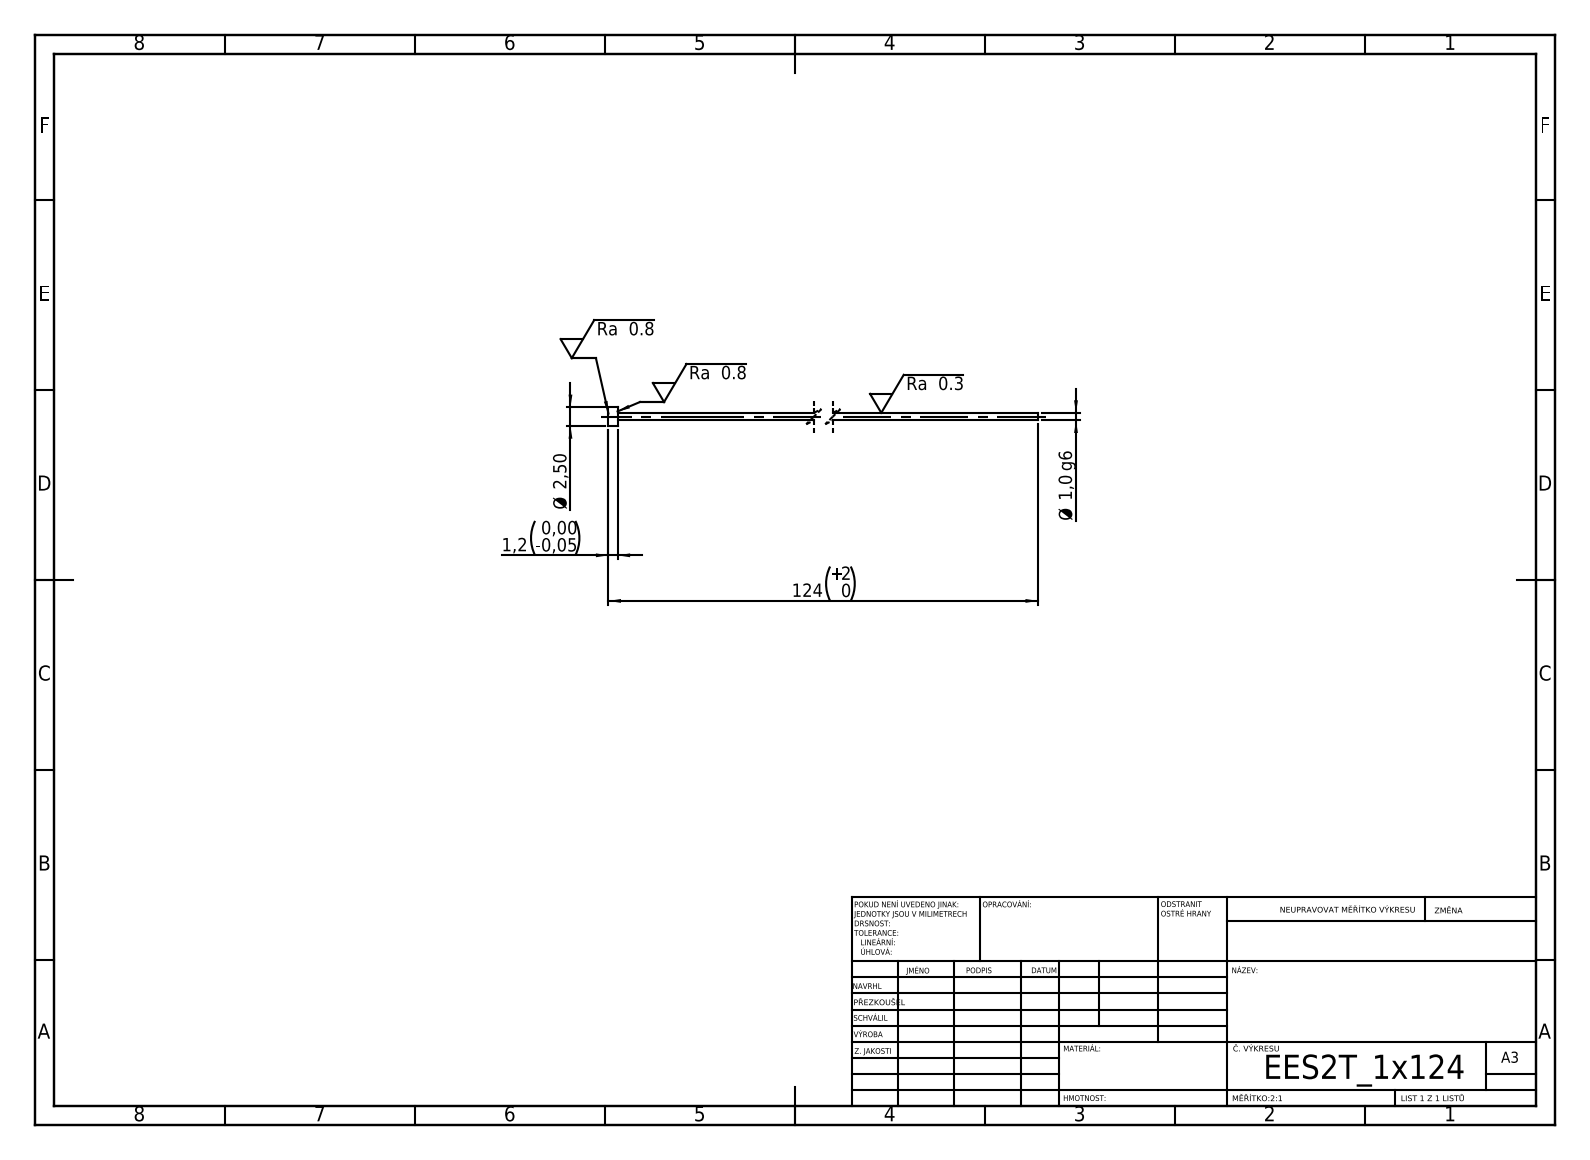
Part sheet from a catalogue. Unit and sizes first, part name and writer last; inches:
Units: inches
Overall size (bounding box): 4.882 × 0.098 × 0.098
Round bosses / shafts (diameter × count): ⌀0.098 ×1, ⌀0.039 ×1
Main face-to-face distances: 0.047, 4.882, 4.835
Volume: 0.006 in³ · Surface area: 0.628 in²
Bodies: 1 solid, 7 faces (3 planar, 4 cylindrical, 0 other)
STEP written by: SolidWorks 2019 (CONFIG_CONTROL_DESIGN)
